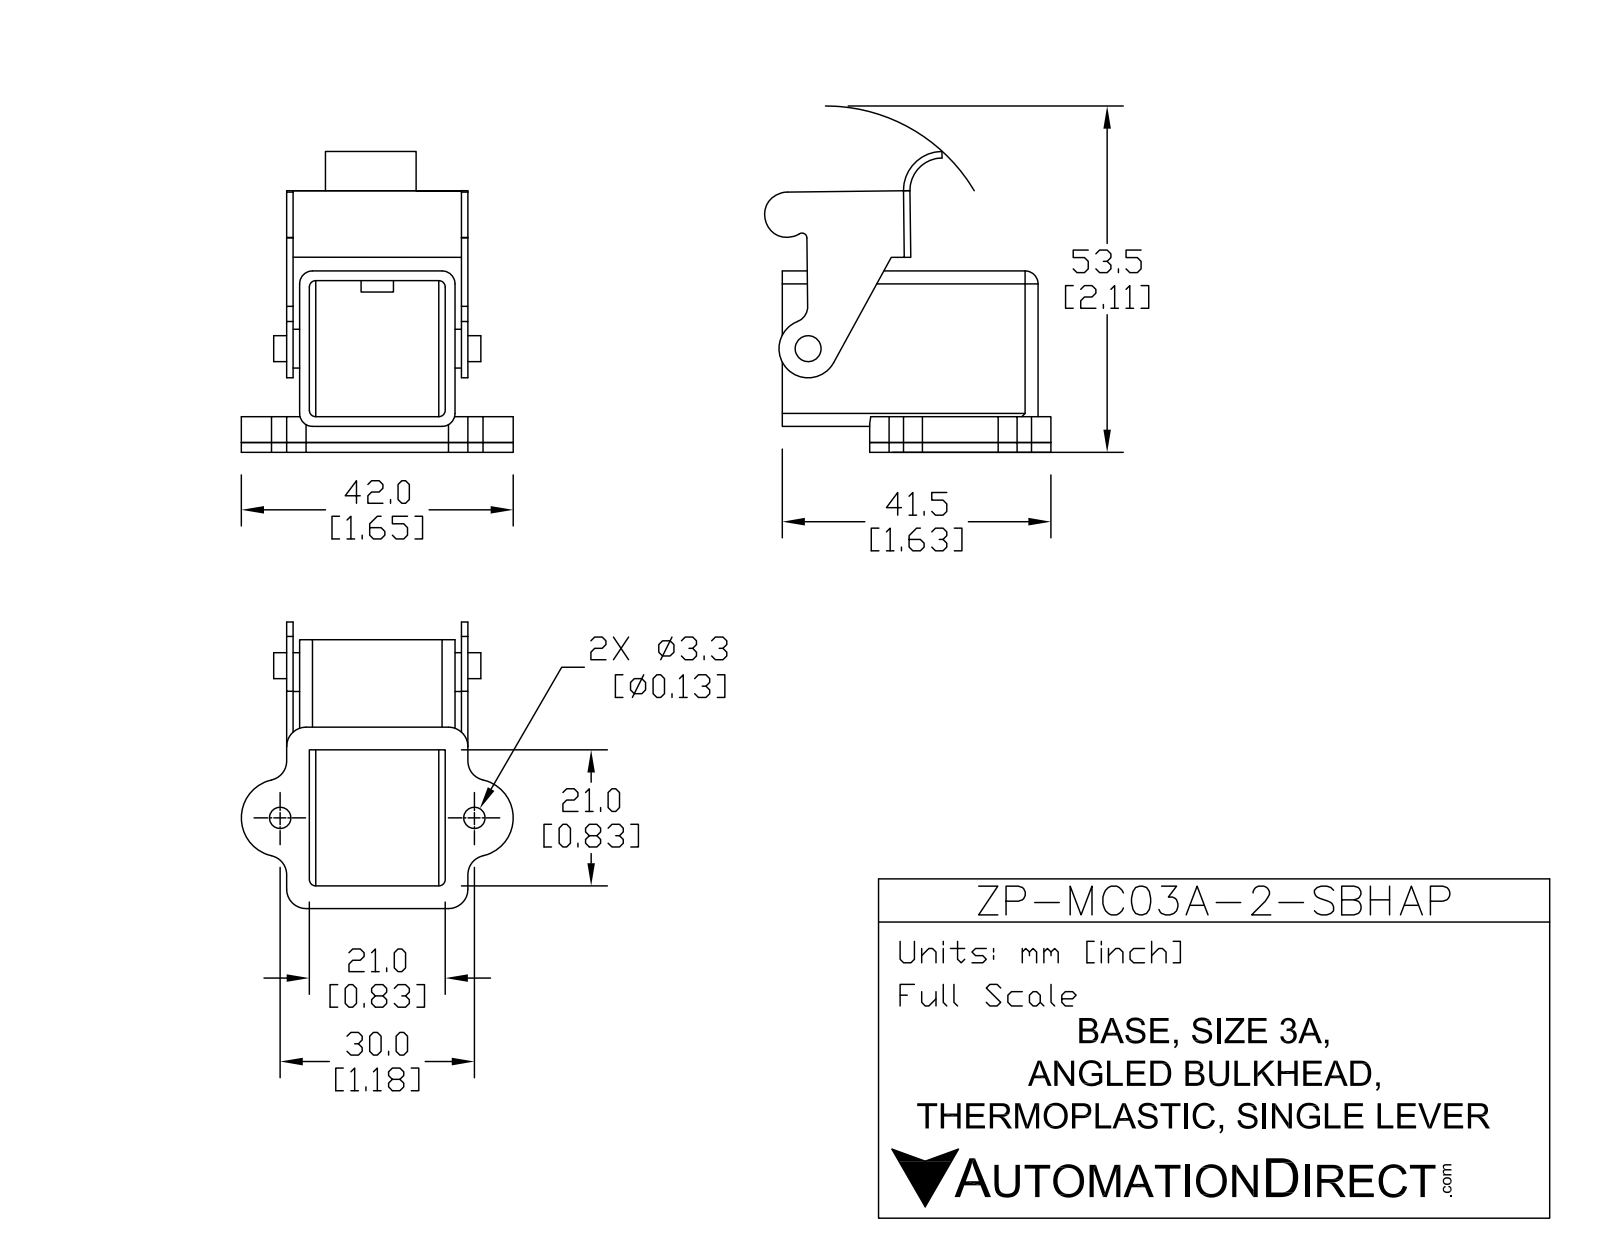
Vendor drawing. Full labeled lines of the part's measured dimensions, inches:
Part name (STEP PRODUCT): ZP-MC03A-2-SBHAP
STEP written by: SolidWorks 2011 (AUTOMOTIVE_DESIGN)
Units: inches
Bodies: 2 solids, 123 faces (53 planar, 65 cylindrical, 5 other)
Overall size (bounding box): 2.149 × 1.905 × 1.654
Volume: 0.646 in³ · Surface area: 19.47 in²
Round holes (diameter × count): ⌀0.13 ×2, ⌀0.118 ×1
Round bosses / shafts (diameter × count): ⌀0.236 ×1, ⌀0.157 ×1
Partial cylindrical surfaces — rounded edges, fillets, slot ends (radius × count): R0.079 ×13, R0.118 ×8, R0.039 ×6, R0.236 ×2, R0.02 ×1, R0.039 ×1, R0.136 ×1, R0.147 ×1
Main face-to-face distances: 0.059, 0.886, 0.827, 0.984, 1.043, 0.945, 0.157, 0.098, 0.101, 0.039
Hole centre spacings: 0.878, 1.181
